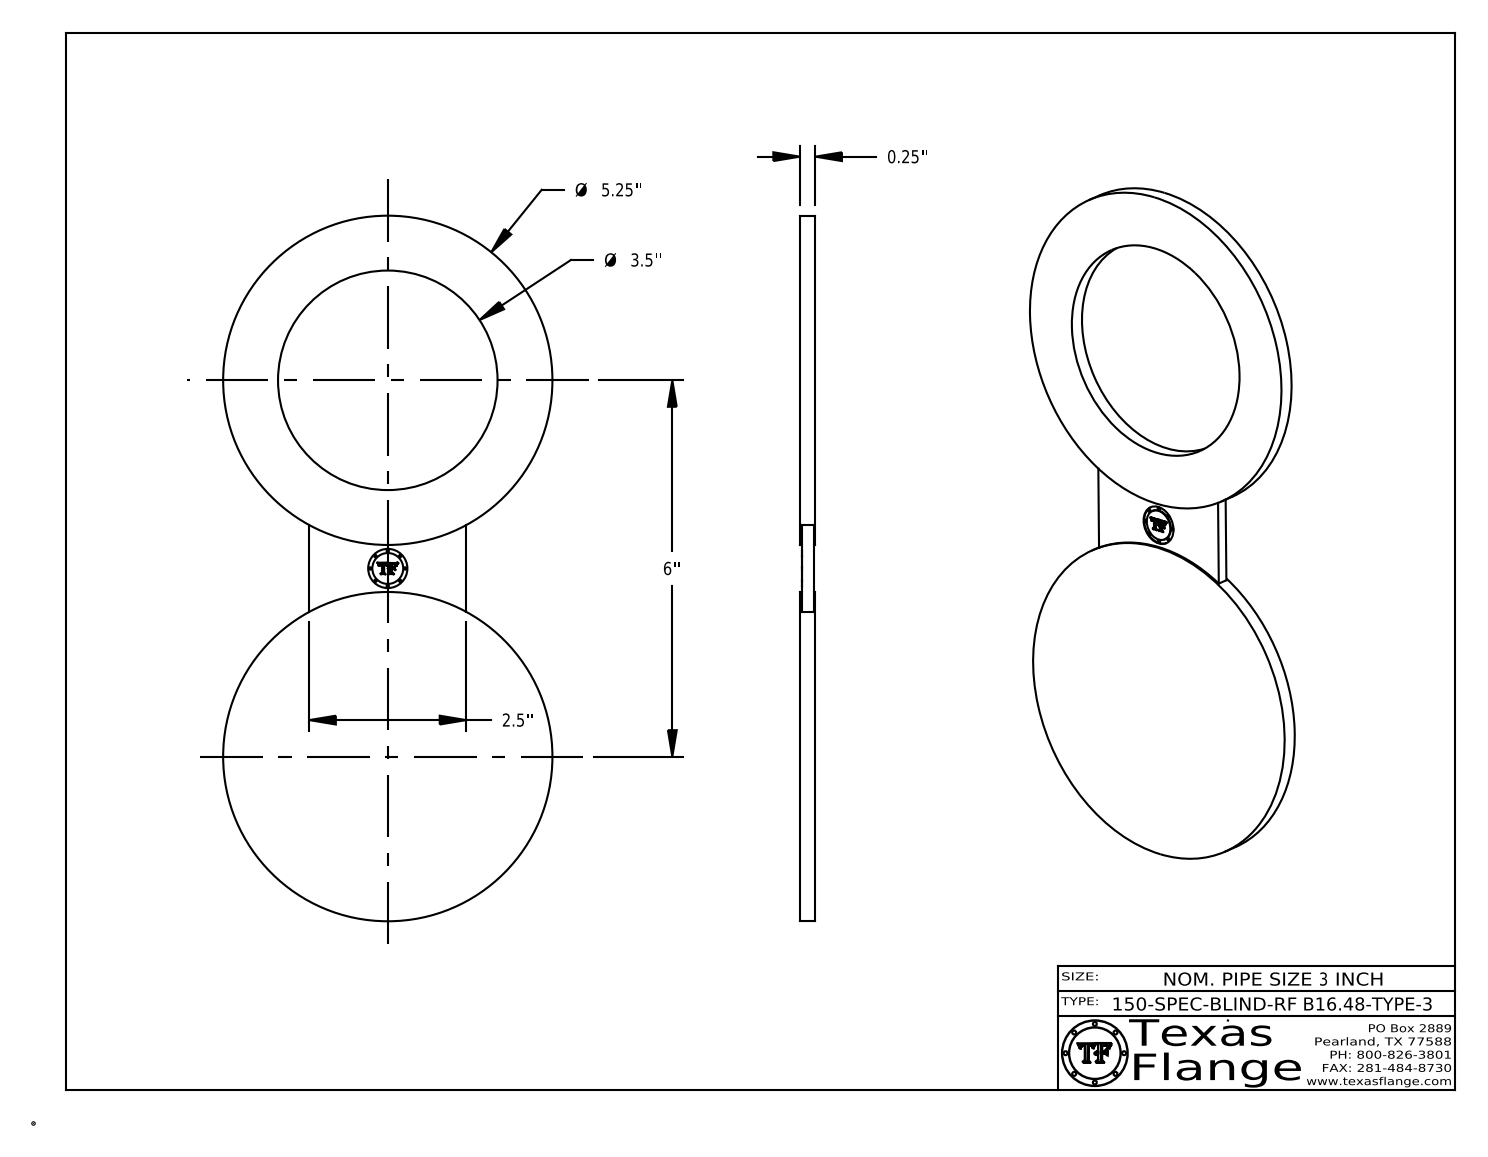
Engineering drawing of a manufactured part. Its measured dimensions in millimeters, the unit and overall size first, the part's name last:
Units: millimetres
Overall size (bounding box): 285.8 × 133.4 × 6.4
Round holes (diameter × count): ⌀15.9 ×1, ⌀88.9 ×1
Round bosses / shafts (diameter × count): ⌀1 ×8, ⌀133.4 ×2, ⌀12.5 ×1
Main face-to-face distances: 6.4, 5.6, 0.8, 4.7, 63.5, 1.2, 5.2, 4.4, 0.4, 30.1
Hole centre spacings: 76.2
Volume: 145 300 mm³ · Surface area: 53 410 mm²
Bodies: 1 solid, 399 faces (373 planar, 26 cylindrical, 0 other)
Part name (STEP PRODUCT): 3-150-SPEC-BLIND-RF-B16.48-TYPE-3
STEP written by: CATIA V5 STEP AP214 (AUTOMOTIVE_DESIGN)
